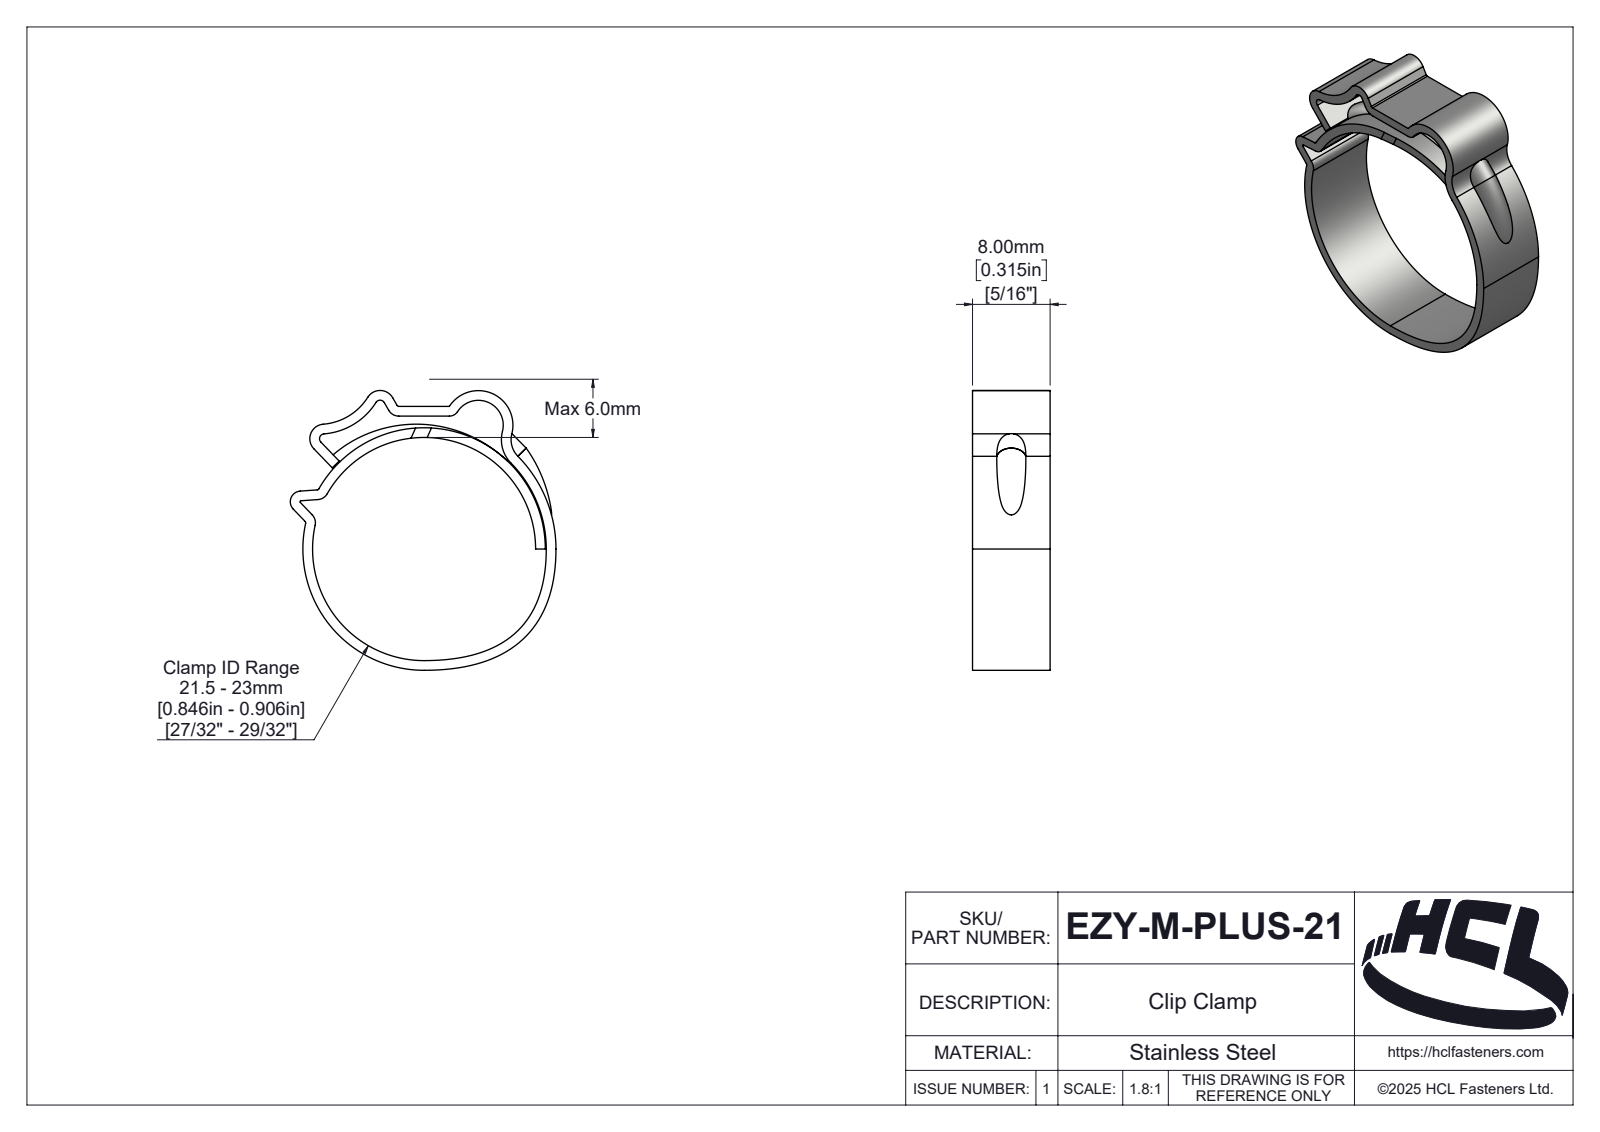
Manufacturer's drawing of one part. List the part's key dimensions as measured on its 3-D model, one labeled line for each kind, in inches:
Part name (STEP PRODUCT): EZY-M-PLUS-21
STEP written by: SolidWorks 2025 (AUTOMOTIVE_DESIGN)
Units: inches
Bodies: 2 solids, 171 faces (21 planar, 86 cylindrical, 64 other)
Overall size (bounding box): 1.135 × 1.079 × 0.315
Volume: 0.058 in³ · Surface area: 3.342 in²
Partial cylindrical surfaces — rounded edges, fillets, slot ends (radius × count): R0.008 ×3, R0.047 ×3, R0.02 ×2, R0.059 ×2, R0.394 ×2, R0.004 ×1, R0.009 ×1, R0.037 ×1
Main face-to-face distances: 0.315, 0.039, 0.539, 0.579
